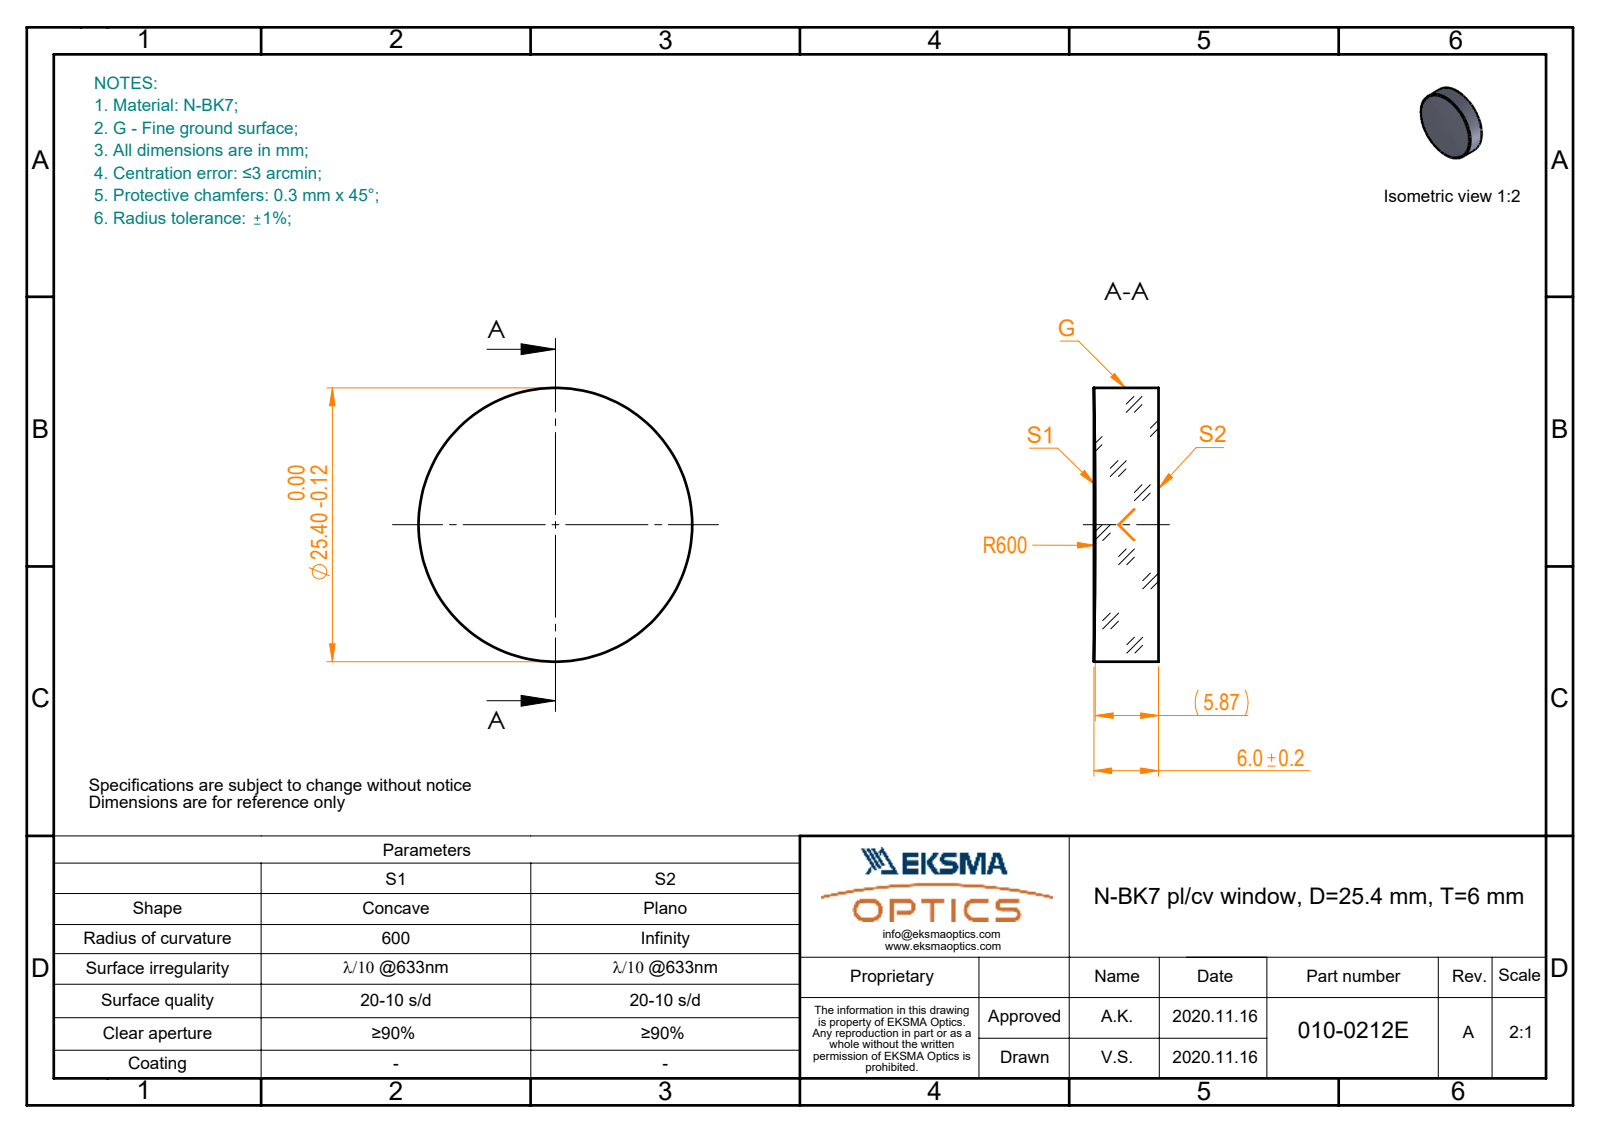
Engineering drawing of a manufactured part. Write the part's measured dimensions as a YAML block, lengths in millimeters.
part_name: "010-0212E_N-BK7_PCV_window"
step_written_by: "SolidWorks 2019 (CONFIG_CONTROL_DESIGN)"
units: millimeters
bodies: {solids: 1, faces: 5, planar: 1, cylindrical: 2, other: 2}
overall_size: [25.4, 25.4, 6]
volume: 3006
surface_area: 1492
round_bosses_or_shafts:
  - {diameter: 25.4, count: 1}
